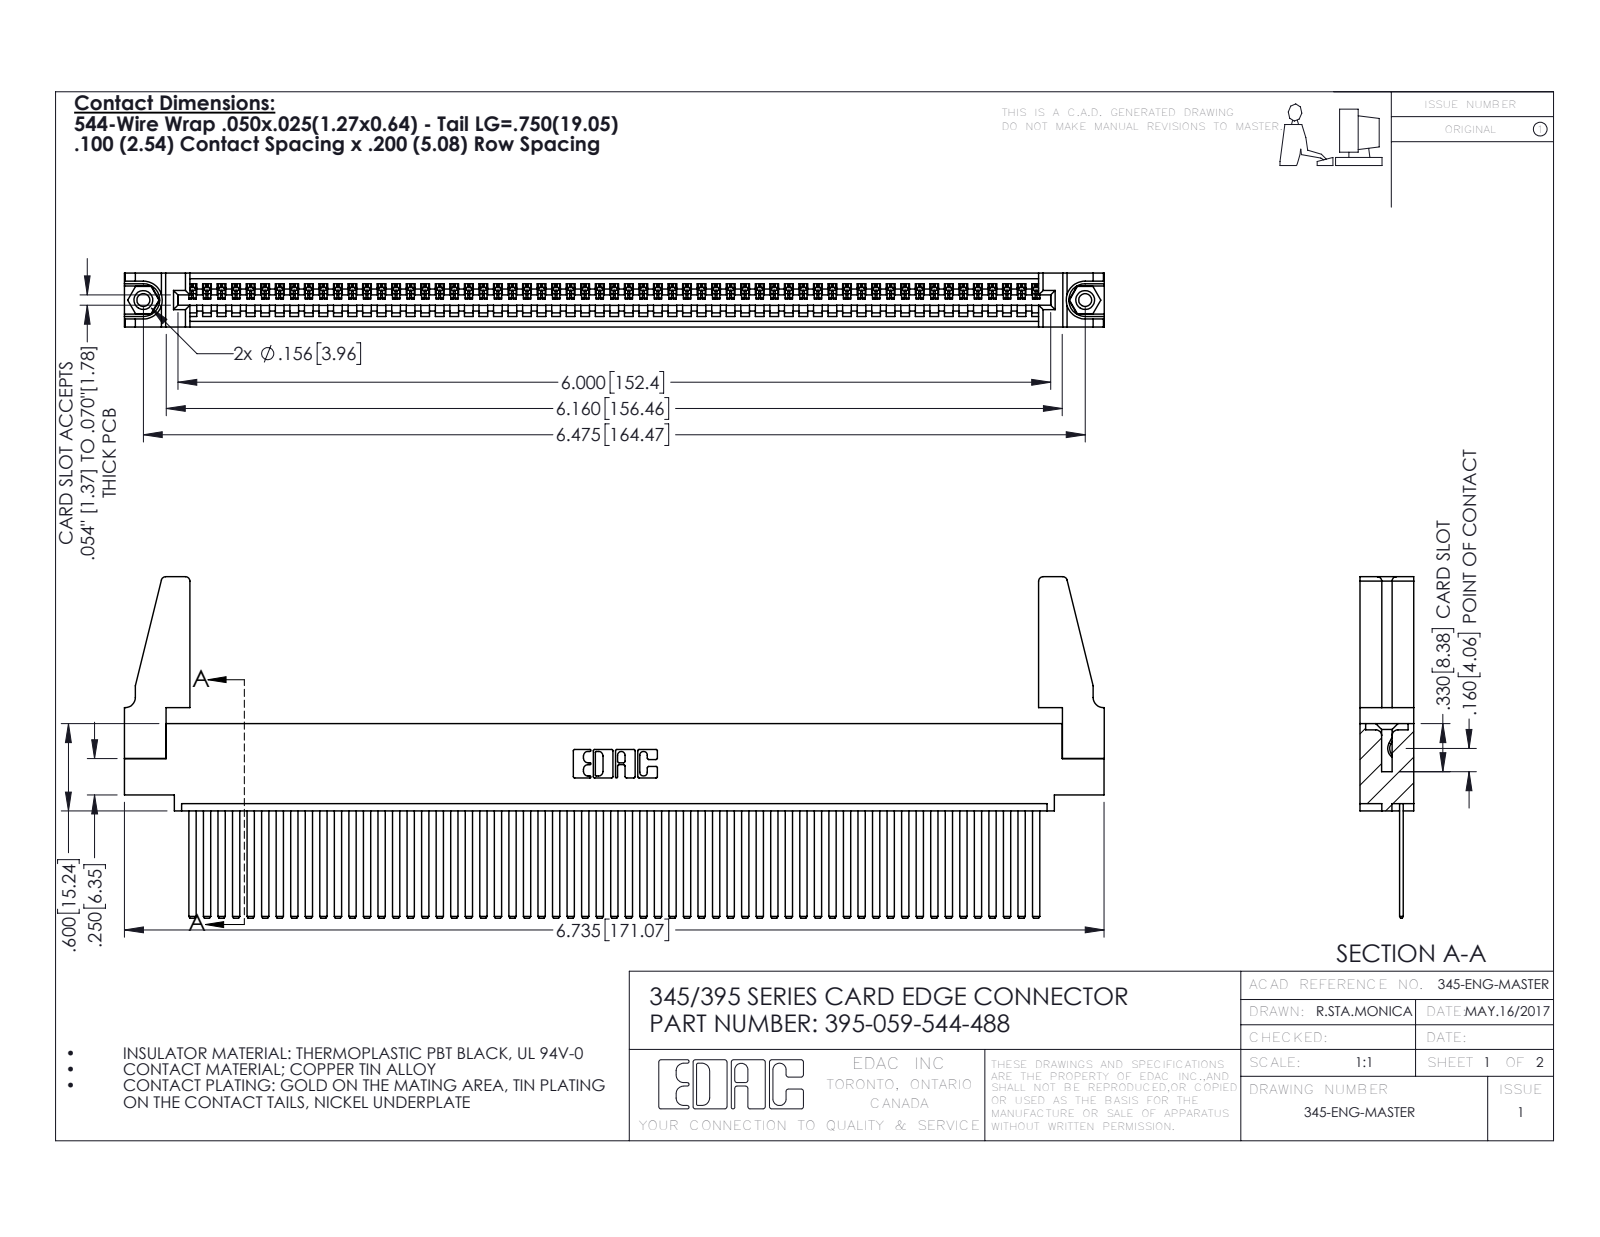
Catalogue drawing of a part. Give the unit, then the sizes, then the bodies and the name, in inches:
Units: inches
Overall size (bounding box): 6.736 × 2.347 × 0.37
Round holes (diameter × count): ⌀0.089 ×2, ⌀0.125 ×2, ⌀0.156 ×2, ⌀0.064 ×1
Round bosses / shafts (diameter × count): ⌀0.155 ×2
Partial cylindrical surfaces — rounded edges, fillets, slot ends (radius × count): R0.006 ×118, R0.01 ×22, R0.03 ×8, R0.007 ×6, R0.031 ×6, R0.026 ×3, R0.031 ×2, R0.04 ×2
Main face-to-face distances: 0.072, 0.298, 0.098, 0.272, 0.025, 0.37, 0.2, 0.225, 0.149, 0.072
Hole centre spacings: 0.27, 6.239, 6.475
Volume: 1.236 in³ · Surface area: 43.53 in²
Bodies: 64 solids, 3322 faces (2280 planar, 1026 cylindrical, 16 other)
Part name (STEP PRODUCT): 345-250-001_345-250-001-102; 345-292-001_345-293-144; 345 Part_0.110 Offset - 0.156 Dia-TH; 345-220-078_345-220-088 (+1 more)
STEP written by: SolidWorks 2016 (CONFIG_CONTROL_DESIGN)
